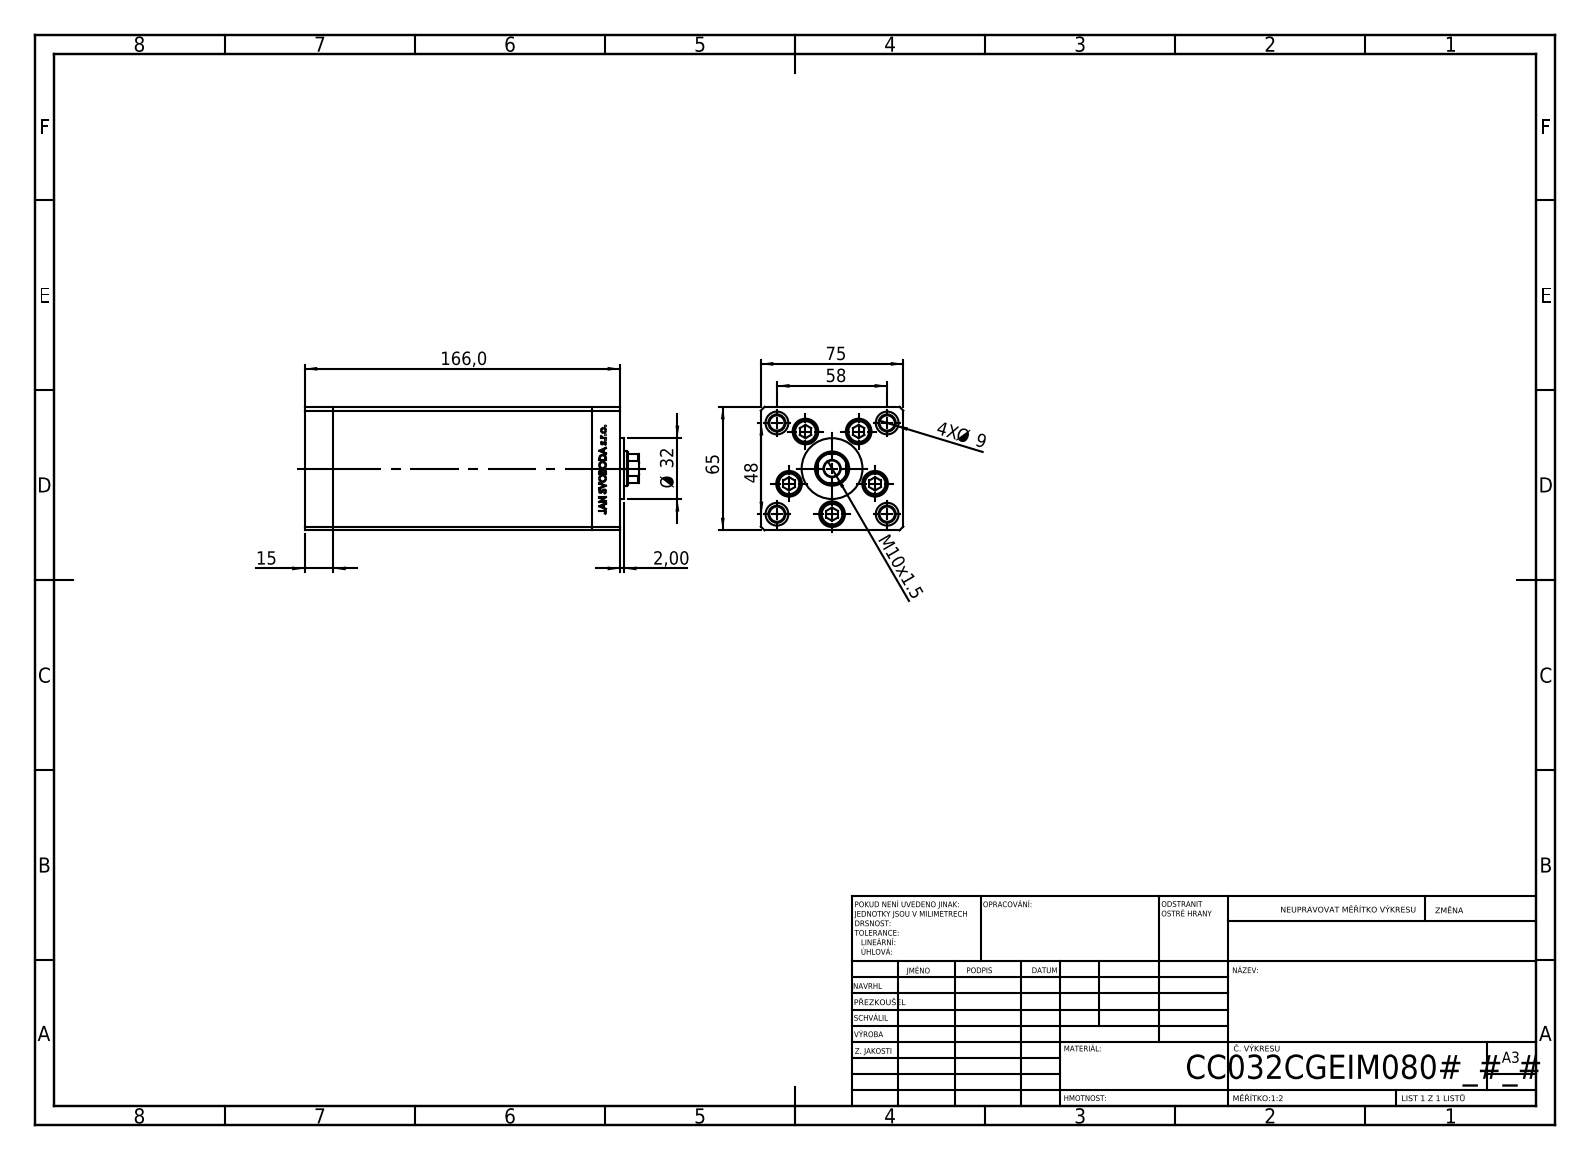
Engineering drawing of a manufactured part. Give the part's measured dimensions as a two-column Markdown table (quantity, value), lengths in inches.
| quantity | value |
| --- | --- |
| part name | V220C_C MIDDLE; ALLEN BOLT; V220C BACK_C; V220C FRONT (+1 more) |
| STEP written by | SolidWorks 2019 (CONFIG_CONTROL_DESIGN) |
| units | inches |
| bodies | 13 solids, 1159 faces (538 planar, 159 cylindrical, 462 other) |
| overall size | 6.929 × 2.953 × 2.559 |
| volume | 41.75 in³ |
| surface area | 219 in² |
| round holes (diameter × count) | 0.354 × 9, 0.531 × 5, 0.315 × 4, 0.472 × 4, 0.335 × 1, 0.492 × 1, 0.709 × 1 |
| round bosses / shafts (diameter × count) | 0.315 × 5, 0.492 × 4, 1.26 × 1 |
| partial cylindrical surfaces (radius × count) | 0.037 × 2, 0.335 × 1 |
| main face-to-face distances | 2.953, 2.559, 0.591, 5.354, 5.945, 6.535, 1.102, 5.591, 0.354, 2.146 |
| hole center spacings | 0.945, 1.482, 0.617, 0.678, 1.091, 1.135, 1.142, 1.285 |
